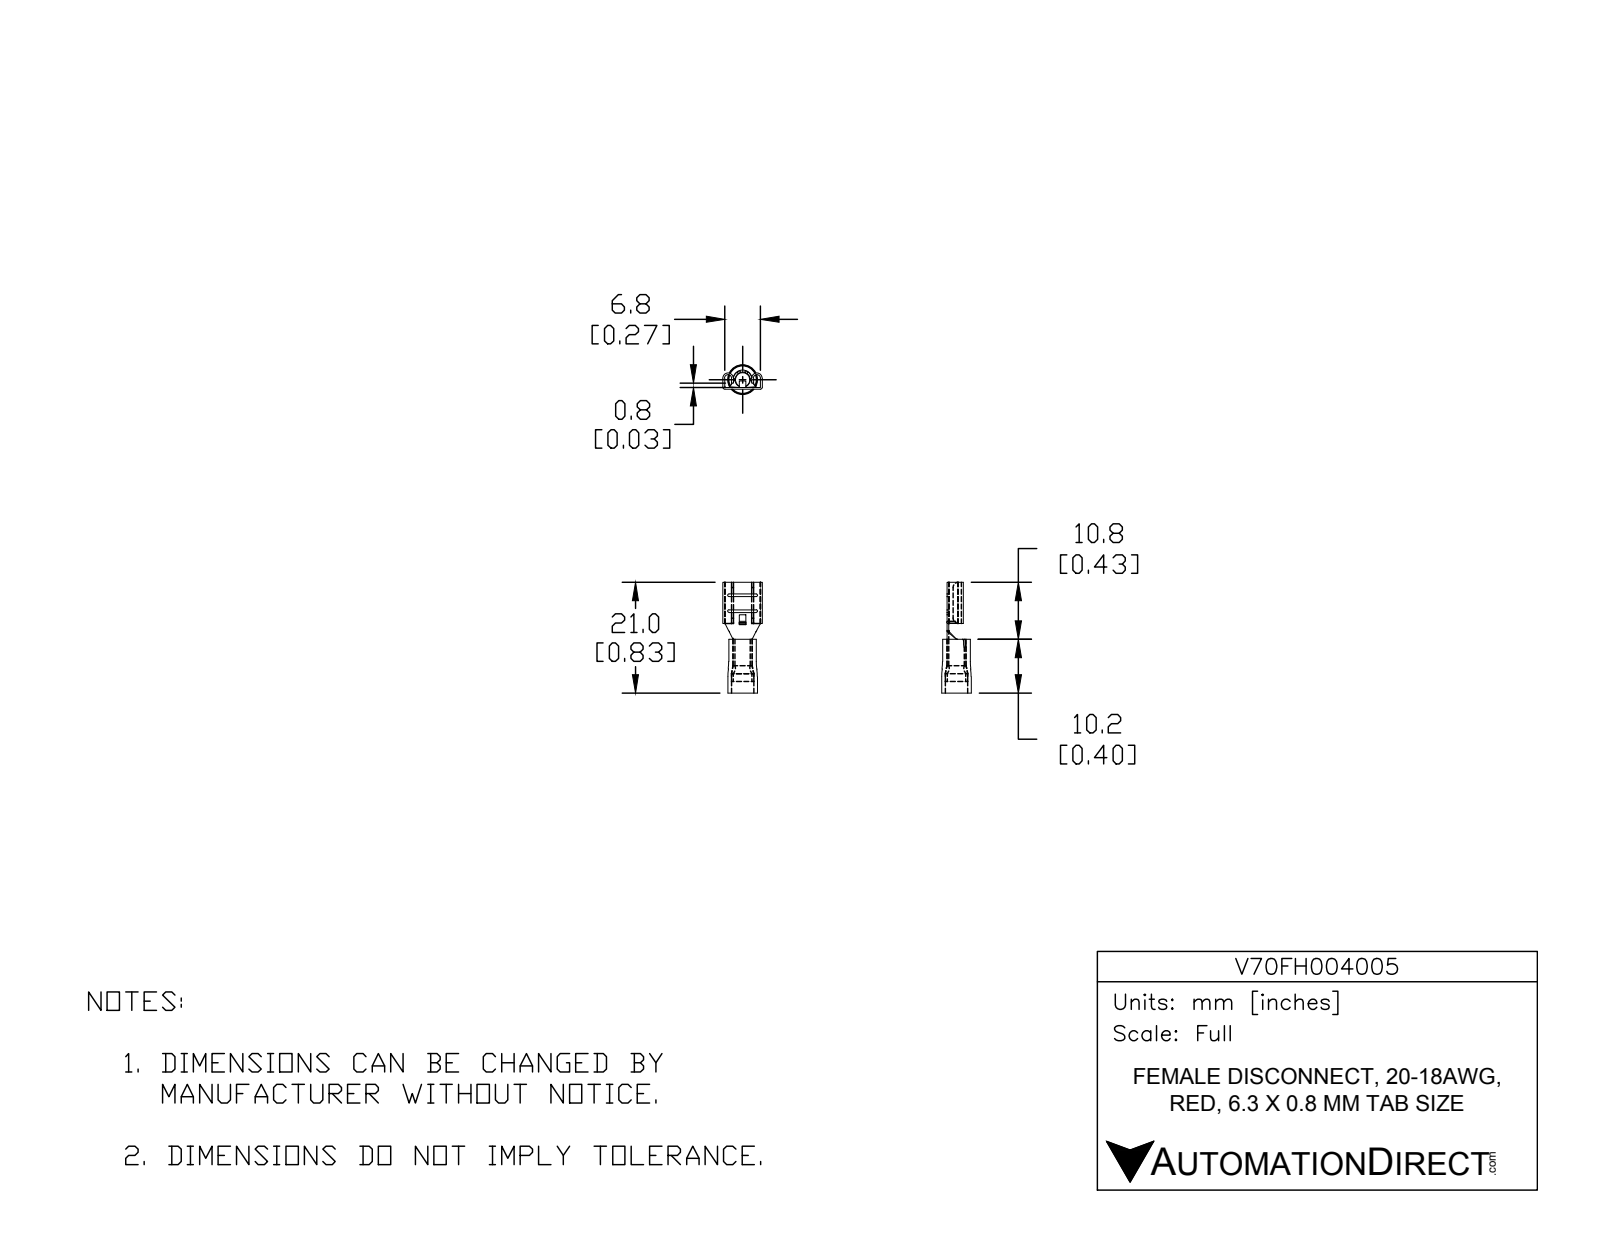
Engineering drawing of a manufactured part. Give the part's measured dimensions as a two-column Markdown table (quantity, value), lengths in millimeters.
| quantity | value |
| --- | --- |
| part name | V70FH004005 |
| STEP written by | SolidWorks 2017 (AUTOMOTIVE_DESIGN) |
| units | millimeters |
| bodies | 2 solids, 102 faces (36 planar, 44 cylindrical, 22 other) |
| overall size | 20.98 × 7.46 × 5.6 |
| volume | 194 mm³ |
| surface area | 821 mm² |
| round holes (diameter × count) | 2.9 × 1, 3.53 × 1, 3.6 × 1, 4.23 × 1 |
| round bosses / shafts (diameter × count) | 5.6 × 1, 5.2 × 1 |
| partial cylindrical surfaces (radius × count) | 0.25 × 6, 0.5 × 4, 1 × 4, 0.38 × 2, 0.65 × 2 |
| main face-to-face distances | 0.35, 1.65, 5.46, 7.11, 2, 5.81, 1.3, 5.11, 3.81, 6.76 |
